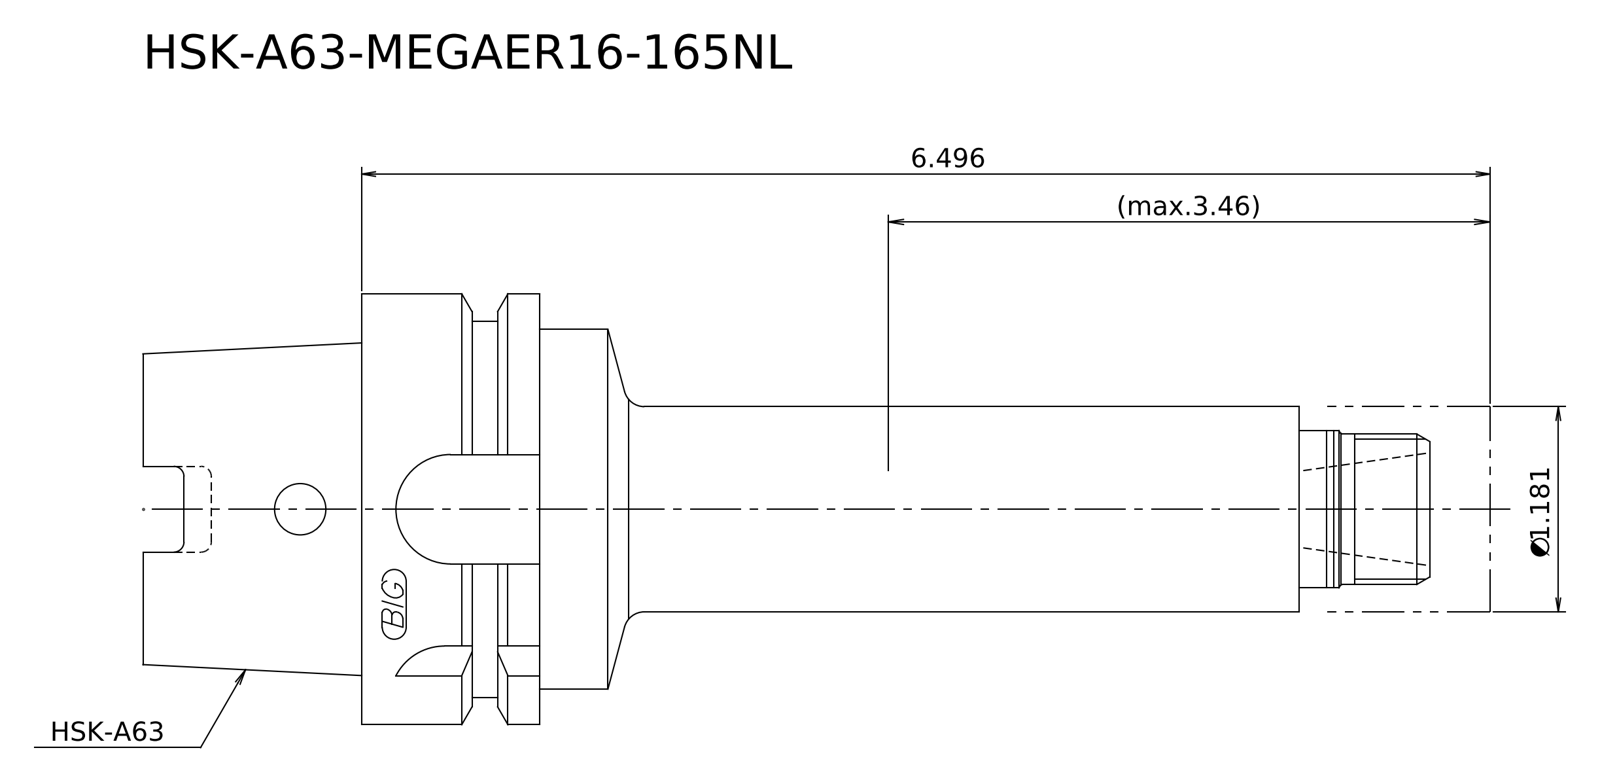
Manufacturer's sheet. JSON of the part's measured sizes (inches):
{"step_written_by": "Kubotek KeyCreator 2011 V10.0.2 (22737) (automotive_design)", "units": "inches", "bodies": {"solids": 2, "faces": 23, "planar": 9, "cylindrical": 8, "other": 6}, "overall_size": [7.756, 2.48, 2.48], "volume_in3": 15.56, "surface_area_in2": 50.66, "round_bosses_or_shafts": [[2.48, 1], [2.165, 1], [2.071, 1], [1.181, 1], [0.906, 1], [0.866, 1]], "face_to_face_distances": [1.26, 1.024, 2.283, 4.488, 5.512, 6.772, 0.984, 5.472, 6.496, 7.756]}
